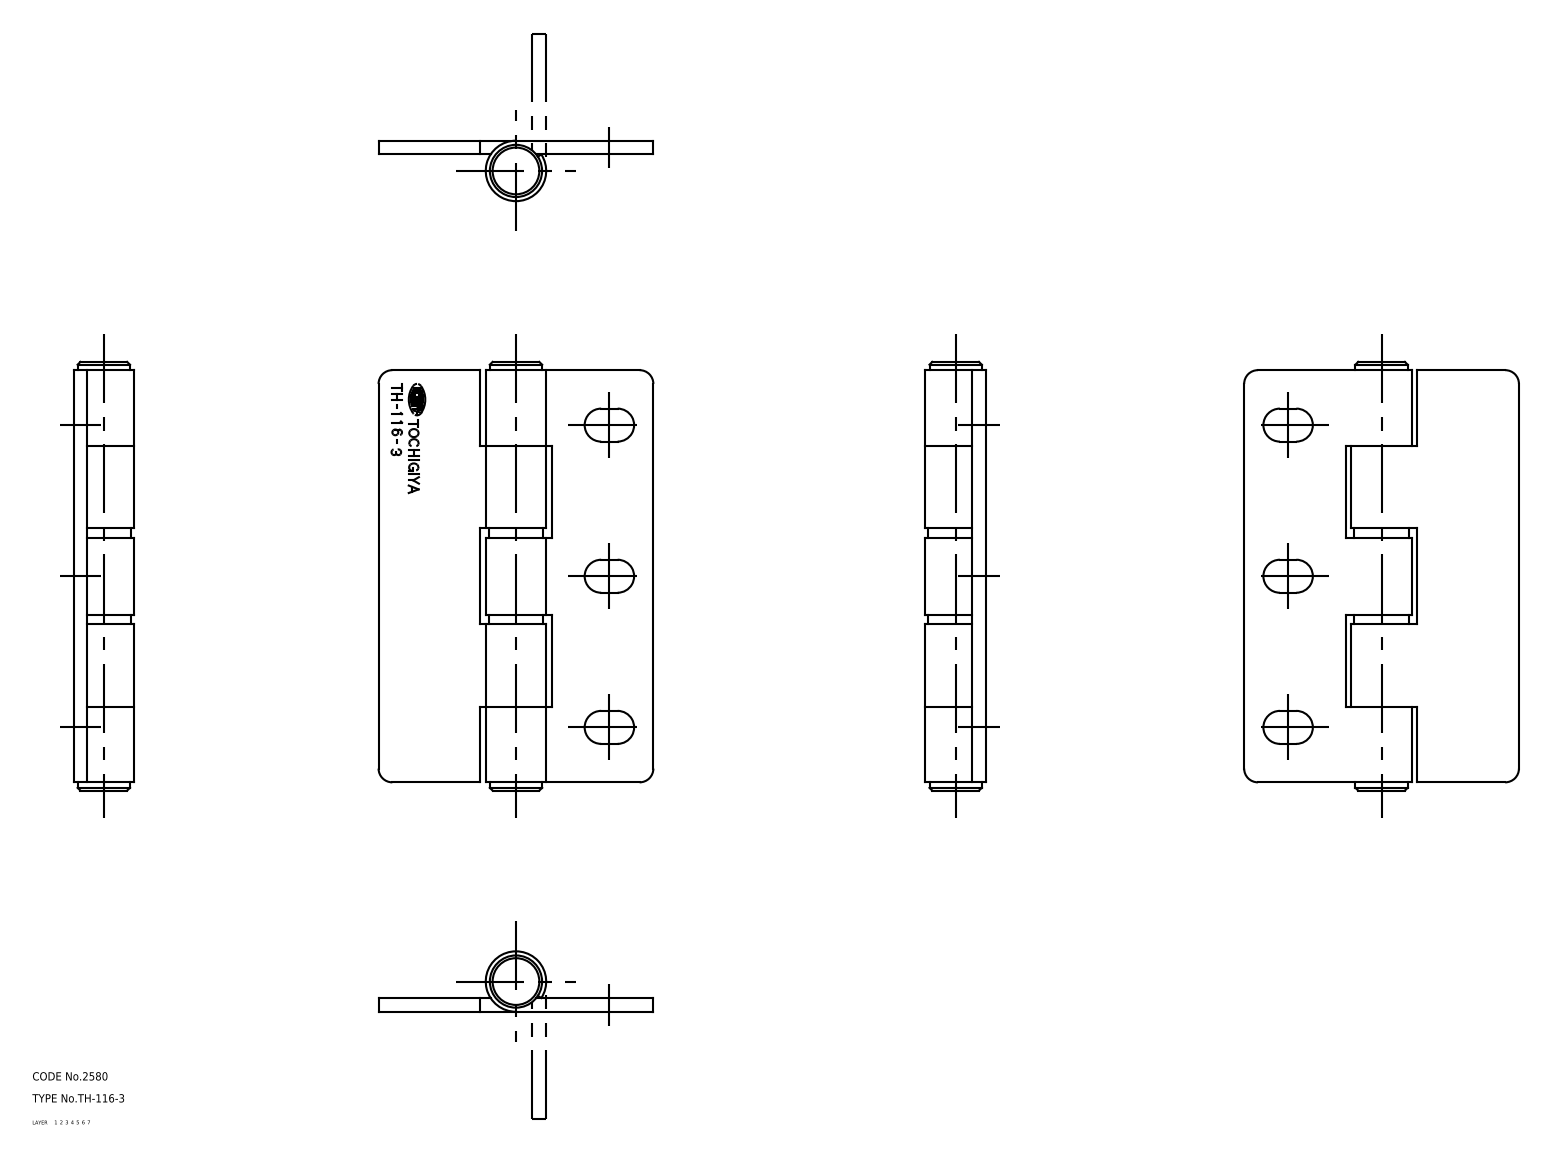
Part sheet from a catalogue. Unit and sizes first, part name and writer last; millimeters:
Units: millimetres
Overall size (bounding box): 156 × 100 × 22
Volume: 114 078 mm³ · Surface area: 53 763 mm²
Bodies: 7 solids, 88 faces (0 planar, 0 cylindrical, 88 other)
Part name (STEP PRODUCT): shaft; cap; bearing; hinge piece_B (+2 more)
STEP written by: CADfix (AUTOMOTIVE_DESIGN)
